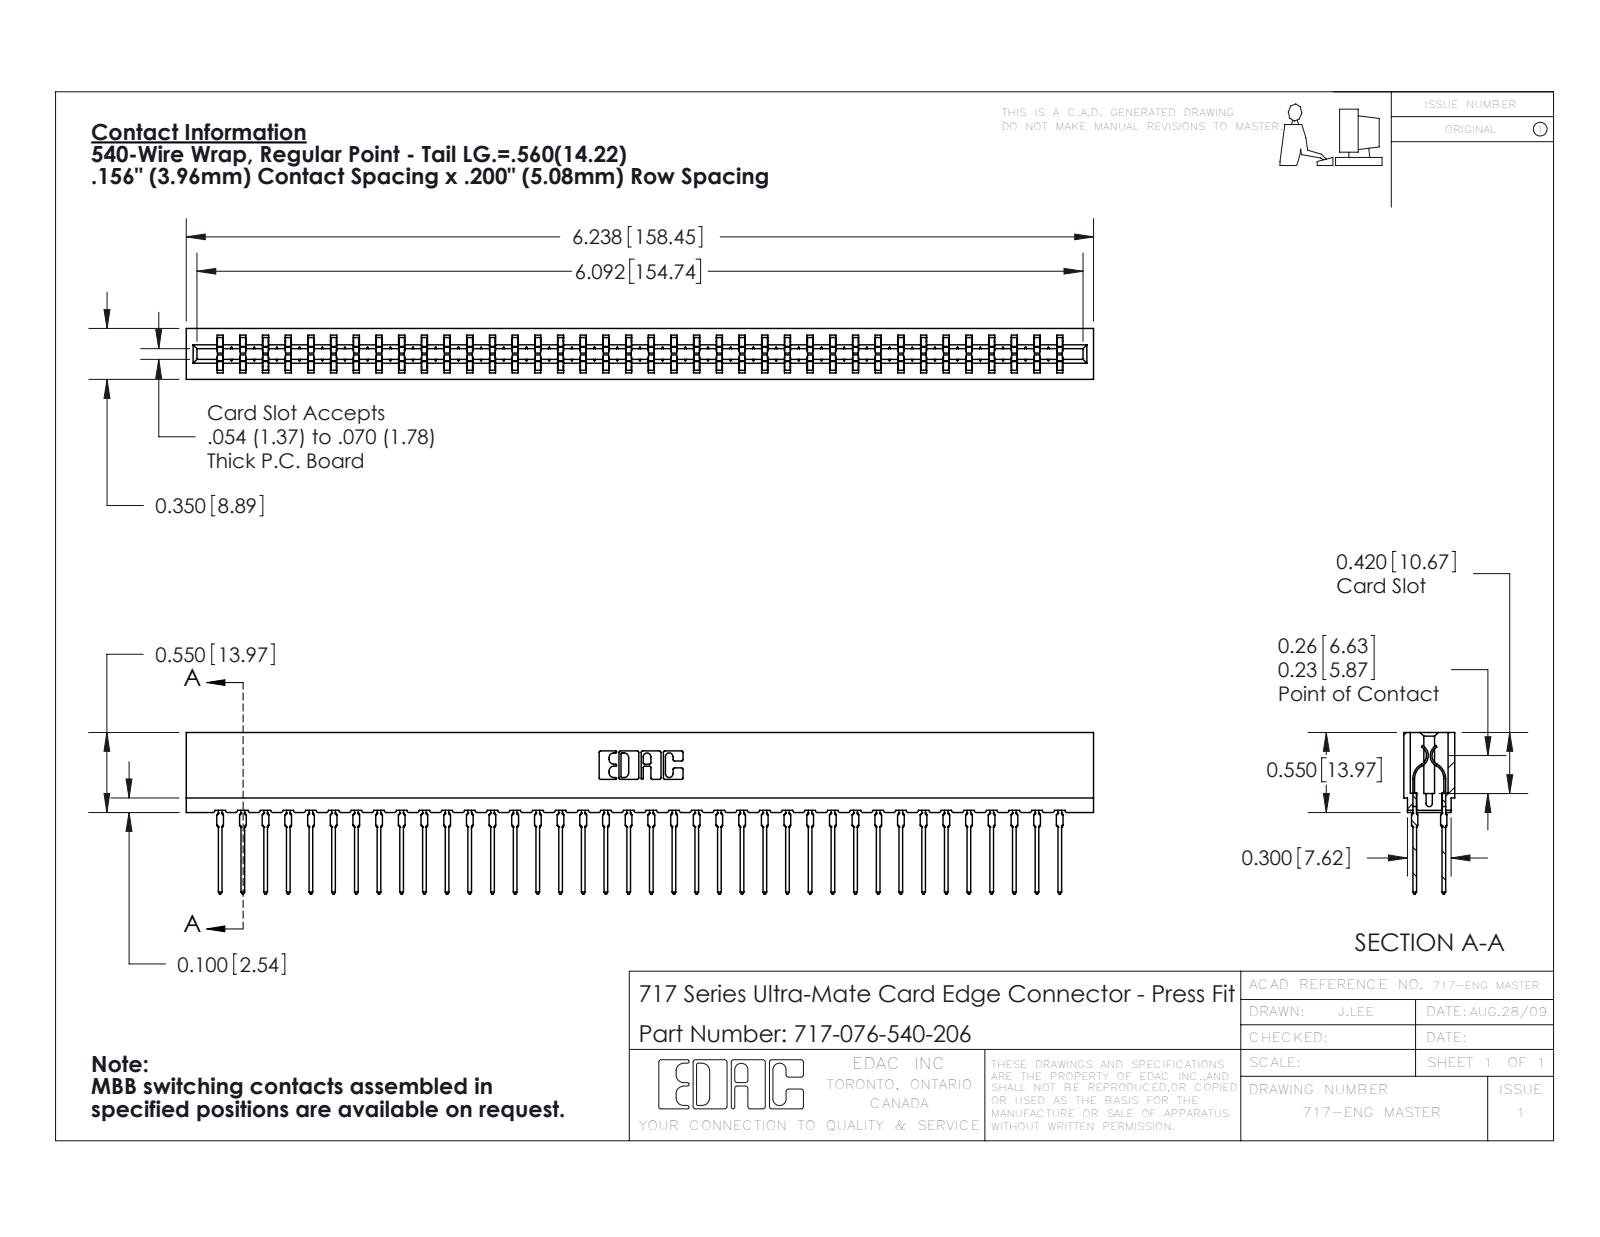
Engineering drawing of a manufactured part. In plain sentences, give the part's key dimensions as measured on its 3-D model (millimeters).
The part is named "717-076-540-206; 745-292-001_540; 717 Part_Insulator Option - 06". Its 3-D file was written by "SolidWorks 2016 (CONFIG_CONTROL_DESIGN)". It is 77 solids with 6934 faces: 3588 planar, 1370 cylindrical and 1976 other. Overall it measures 158.4 by 28.2 by 8.9 millimeters. Its volume is 14 000 cubic millimeters and its surface area 22 300 square millimeters. Partial cylindrical surfaces (rounded edges, fillets, slot ends): 152 of radius 0.5, 76 of radius 0.4, 22 of radius 0.3, 8 of radius 0.1, 8 of radius 0.3, 6 of radius 0.2, 6 of radius 0.8, 3 of radius 0.7. The main face-to-face distances are 5.4, 3.5, 8.9, 1.6, 7.3, 1.9, 3.8, 1.9, 2.2, 6.7.
